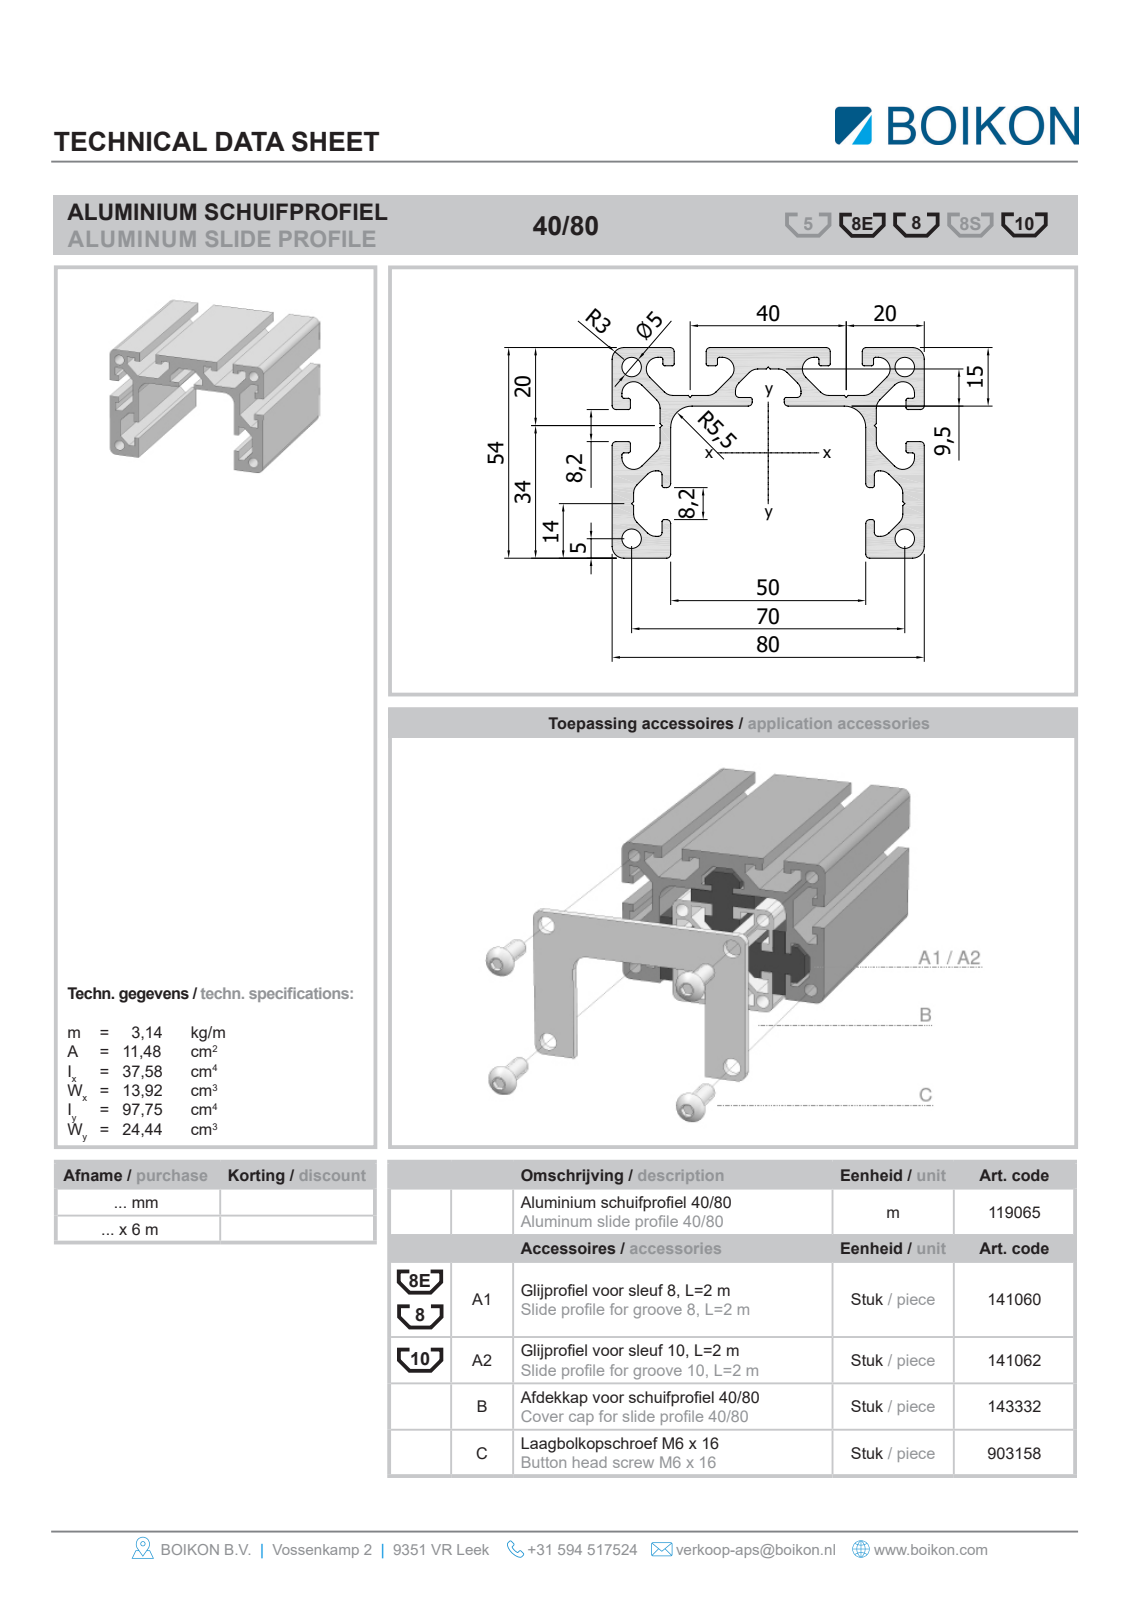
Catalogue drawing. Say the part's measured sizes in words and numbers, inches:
The part is named "Root; 119065Alu Schuifprofiel 40/80BOIKON0". Its 3-D file was written by "HiCAD 2013 1802.4 Build 509 (AUTOMOTIVE_DESIGN)". It is 1 solid with 106 faces: 96 planar, 10 cylindrical and 0 other. Overall it measures 39.37 by 3.15 by 2.126 inches. Its volume is 72.98 cubic inches and its surface area 1 086 square inches. Round holes: 4 of diameter 0.197. Partial cylindrical surfaces (rounded edges, fillets, slot ends): 4 of radius 0.118, 2 of radius 0.217. The main face-to-face distances are 0.591, 0.114, 0.476, 2.559, 3.15, 0.177, 0.362, 0.39, 0.15, 0.122. The hole center spacings are 1.732, 2.756, 3.255.
